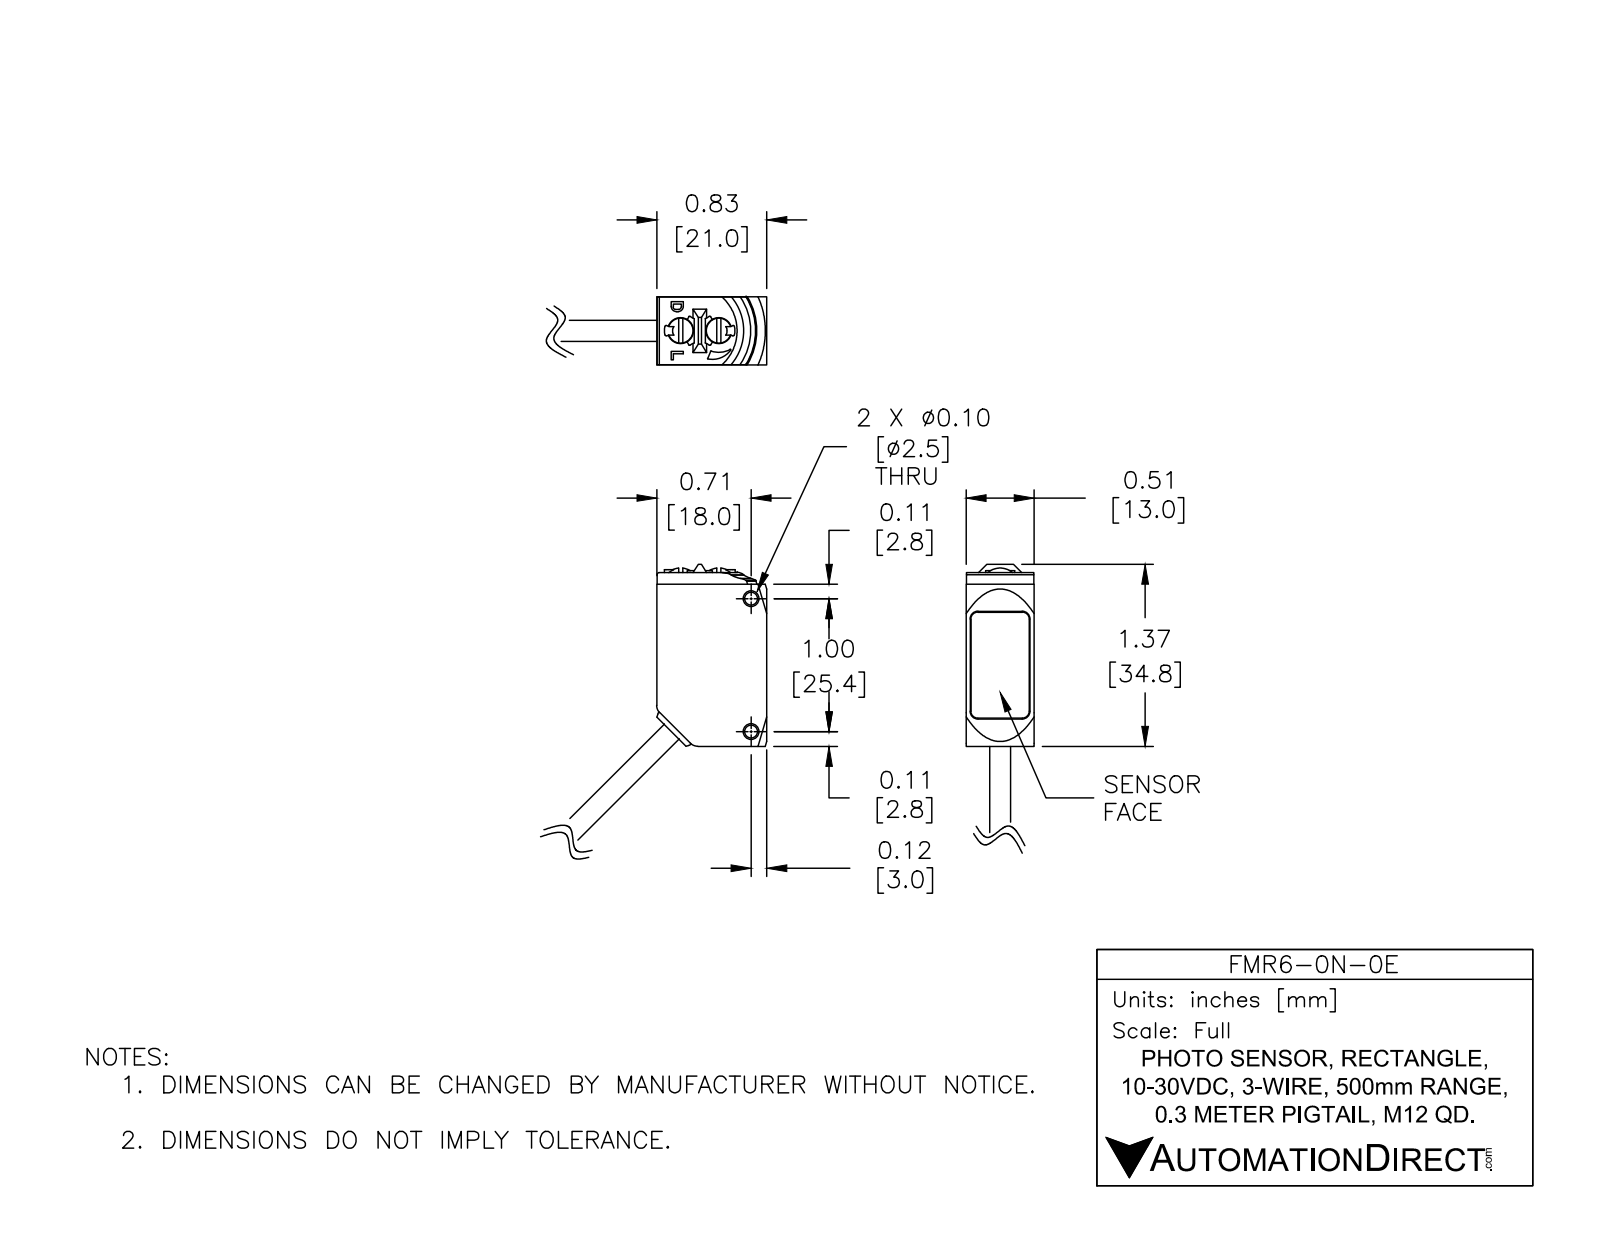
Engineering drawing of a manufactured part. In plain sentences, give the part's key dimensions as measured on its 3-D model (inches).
The part is named "FMR6-0N-0E". Its 3-D file was written by "SolidWorks 2017 (AUTOMOTIVE_DESIGN)". It is 1 solid with 186 faces: 89 planar, 72 cylindrical and 25 other. Overall it measures 2.084 by 1.541 by 0.512 inches. Its volume is 0.542 cubic inches and its surface area 5.476 square inches. Round holes: 2 of diameter 0.097, 2 of diameter 0.197. Round bosses or shafts: 2 of diameter 0.189, 1 of diameter 0.157. Partial cylindrical surfaces (rounded edges, fillets, slot ends): 7 of radius 0.018, 7 of radius 0.02, 4 of radius 0.008, 4 of radius 0.01, 4 of radius 0.051, 4 of radius 0.059, 3 of radius 0.004, 2 of radius 0.018. The main face-to-face distances are 0.512, 0.827, 1.307, 0.035, 0.51, 0.031, 0.48, 0.037, 0.474, 0.472. The hole center spacings are 0.287, 1.
